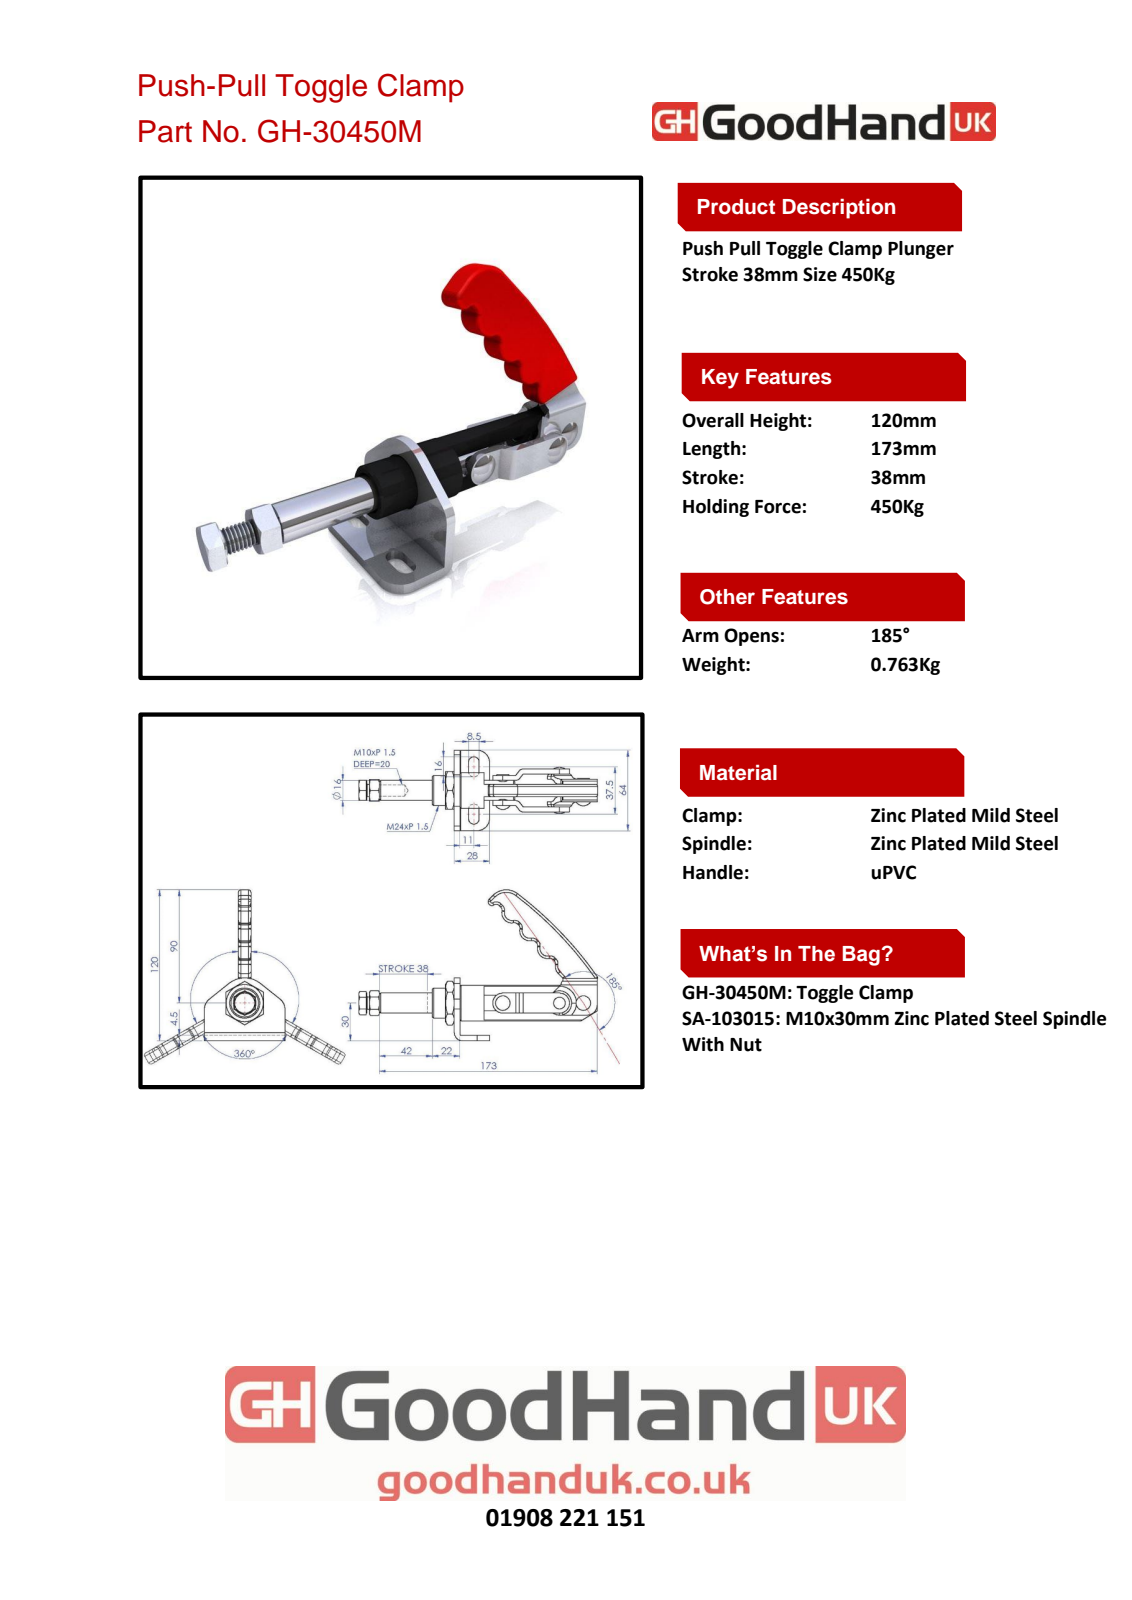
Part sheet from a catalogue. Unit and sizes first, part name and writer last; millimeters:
Units: millimetres
Overall size (bounding box): 190.9 × 125.5 × 64
Round holes (diameter × count): ⌀6 ×3, ⌀8.05 ×2, ⌀8.5 ×1, ⌀9 ×1, ⌀10 ×1, ⌀22 ×1, ⌀25 ×1
Round bosses / shafts (diameter × count): ⌀28.5 ×1, ⌀24 ×1, ⌀16.02 ×1, ⌀16 ×1, ⌀9 ×1, ⌀8 ×1, ⌀6 ×1
Partial cylindrical surfaces — rounded edges, fillets, slot ends (radius × count): R3 ×10, R4 ×4, R4.01 ×4, R4.25 ×4, R8 ×3, R0.5 ×1, R6.5 ×1, R9.5 ×1
Main face-to-face distances: 4, 8, 5, 9, 1, 11.5, 4.5, 15.5, 16.5, 7.5
Hole centre spacings: 19, 45, 64
Volume: 114 461 mm³ · Surface area: 64 487 mm²
Bodies: 8 solids, 369 faces (147 planar, 129 cylindrical, 93 other)
Part name (STEP PRODUCT): Group2^GH-30450M(簡化); Group5^GH-30450M(簡化); GH-30450M(簡化); 13045013(ch-solid-after)-1^GH-30450M(簡化) (+3 more)
STEP written by: SolidWorks 2016 (AUTOMOTIVE_DESIGN)
